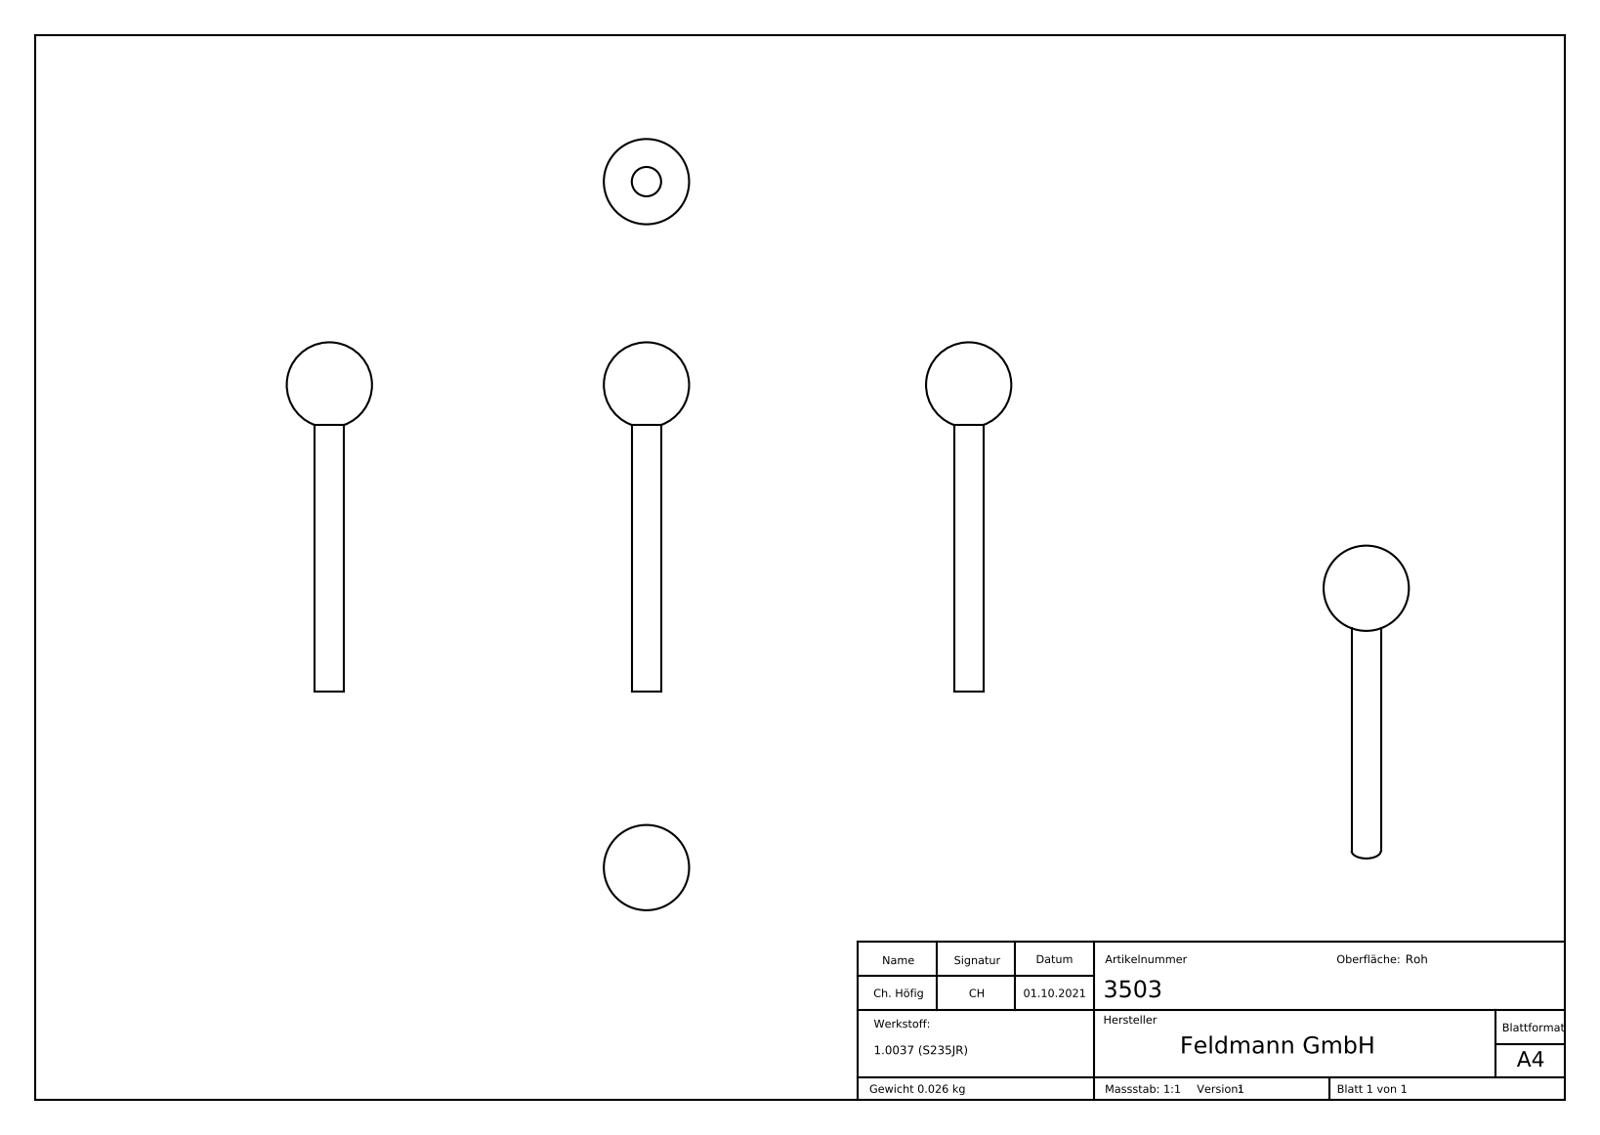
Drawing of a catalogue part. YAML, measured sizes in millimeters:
part_name: "3503"
step_written_by: "SolidWorks 2015 (CONFIG_CONTROL_DESIGN)"
units: millimeters
bodies: {solids: 1, faces: 5, planar: 1, cylindrical: 2, other: 2}
overall_size: [65.51, 16, 16]
volume: 3327
surface_area: 1667
round_bosses_or_shafts:
  - {diameter: 5.5, count: 1}
